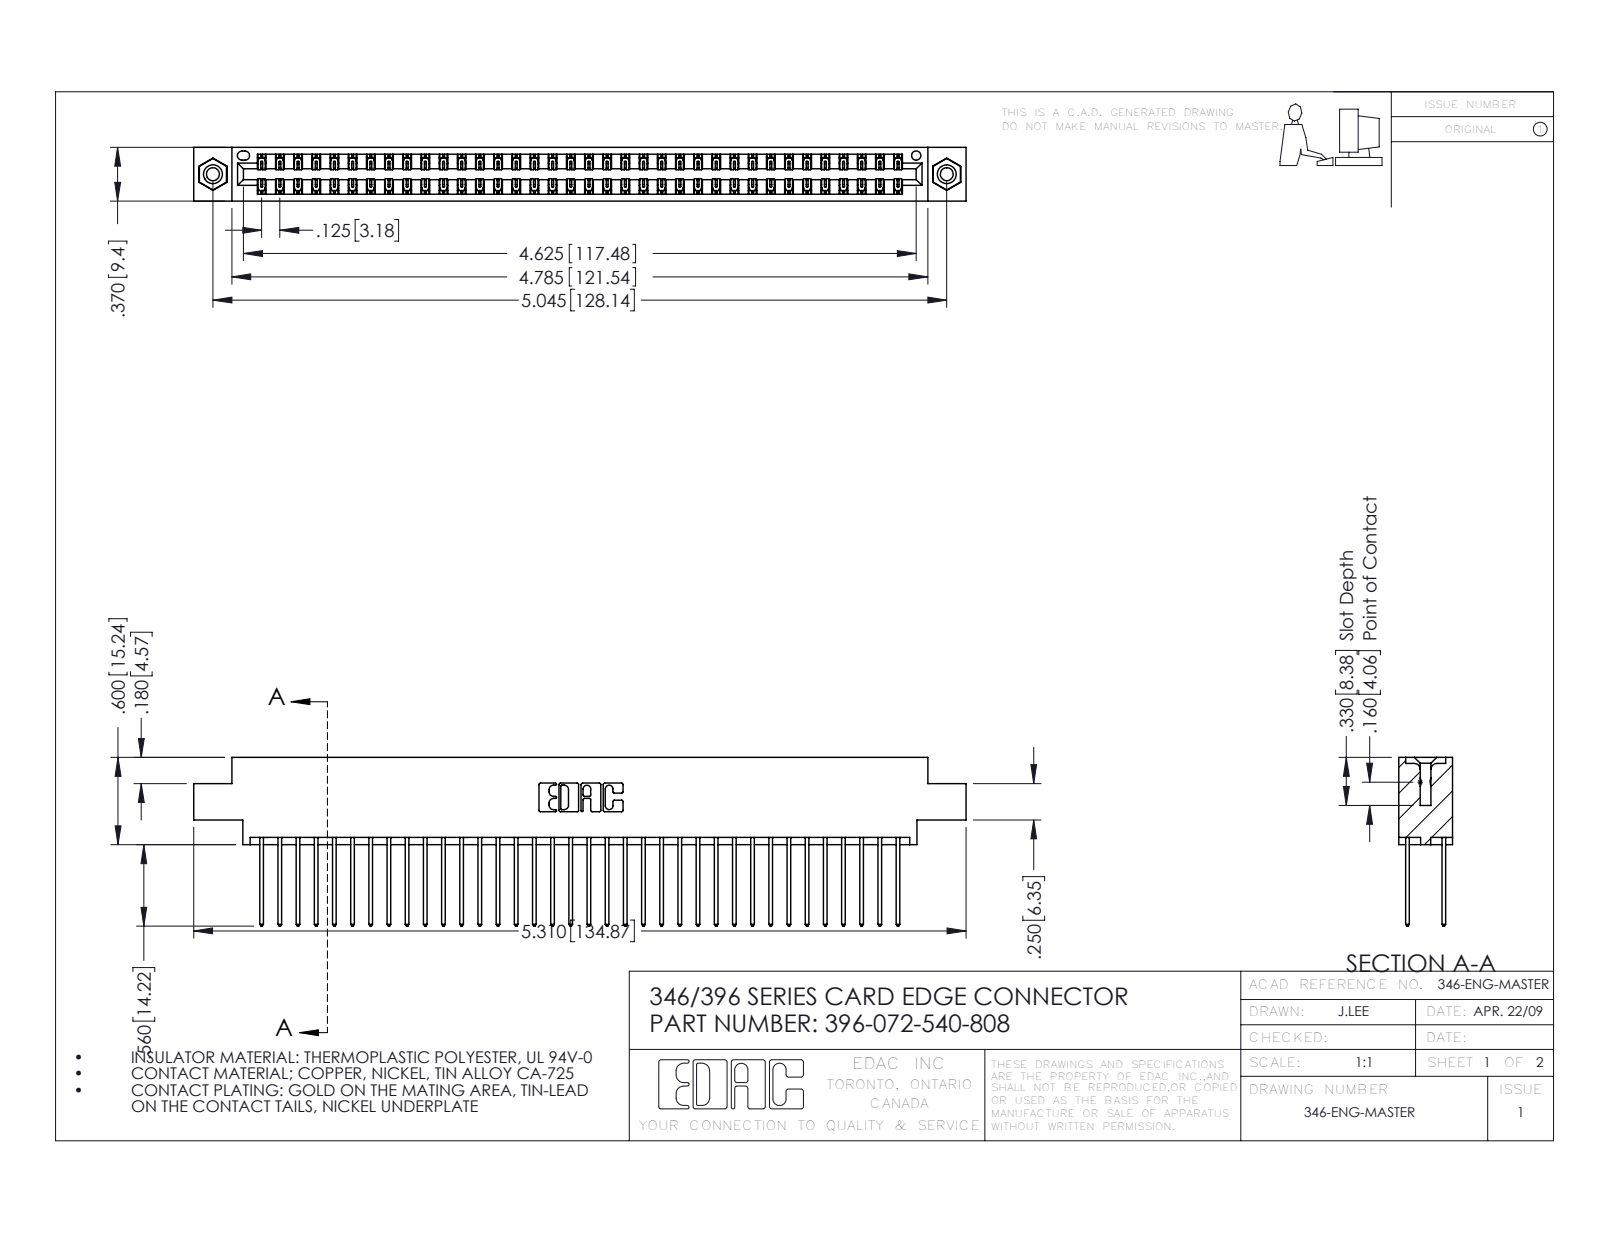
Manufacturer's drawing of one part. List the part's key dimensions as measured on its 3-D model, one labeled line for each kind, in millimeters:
Part name (STEP PRODUCT): 345-292-001_345-293-140; 396-072-540-808; 346 Part_0.170 Offset - 0.156 Dia-TI; 345-250-001_345-250-003-102
STEP written by: SolidWorks 2016 (CONFIG_CONTROL_DESIGN)
Units: millimetres
Bodies: 75 solids, 3930 faces (2632 planar, 1282 cylindrical, 16 other)
Overall size (bounding box): 134.9 × 29.5 × 9.4
Volume: 13 200 mm³ · Surface area: 19 560 mm²
Round holes (diameter × count): ⌀2.3 ×2, ⌀3.2 ×2, ⌀4 ×2, ⌀1.6 ×1
Round bosses / shafts (diameter × count): ⌀3.9 ×2
Partial cylindrical surfaces — rounded edges, fillets, slot ends (radius × count): R0.2 ×108, R0.3 ×72, R0.3 ×22, R0.2 ×6, R0.8 ×6, R0.7 ×3, R0.4 ×2, R0.6 ×2
Main face-to-face distances: 1.2, 8.2, 6.4, 1.8, 7.6, 0.6, 9.4, 7, 5.6, 3.8
Hole centre spacings: 6.2, 122.8, 128.1
